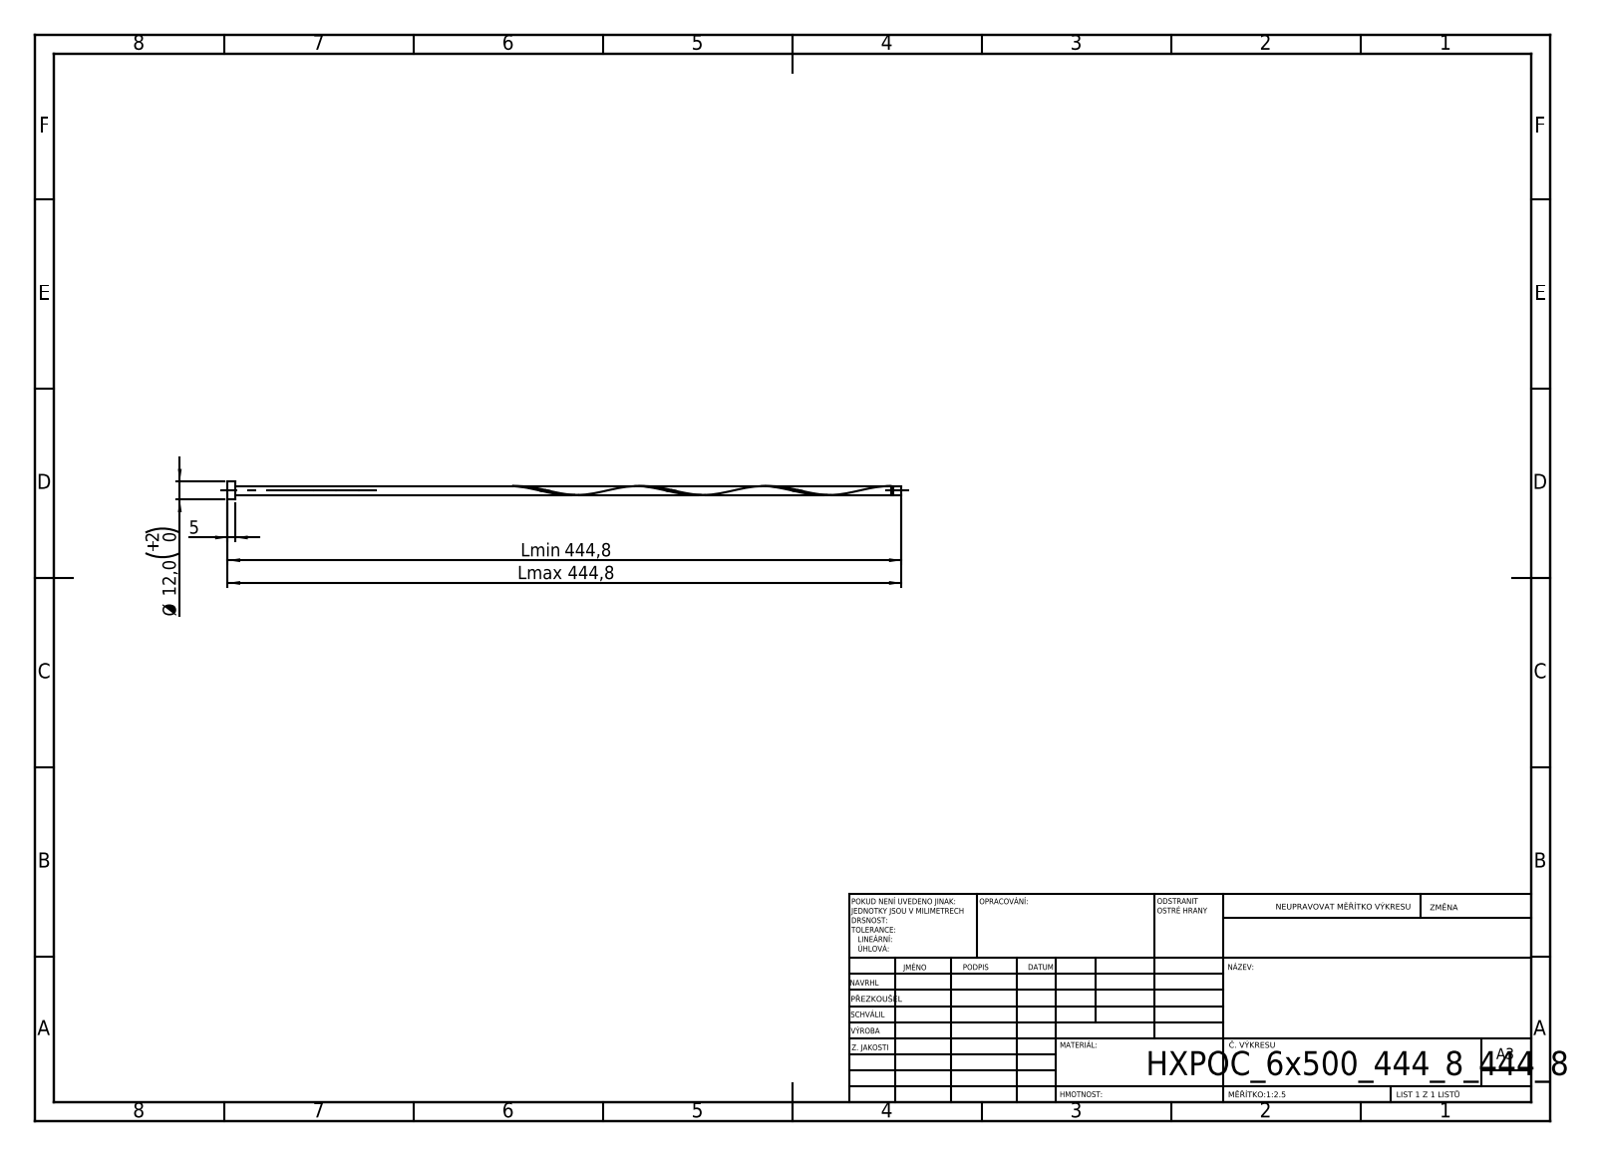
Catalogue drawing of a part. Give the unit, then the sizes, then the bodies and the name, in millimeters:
Units: millimetres
Overall size (bounding box): 444.8 × 12 × 12
Round bosses / shafts (diameter × count): ⌀12 ×1, ⌀6 ×1, ⌀4.8 ×1
Main face-to-face distances: 5, 444.8, 439.8, 438.98, 433.98, 5.82, 437.78, 432.78, 1.2, 7.02
Volume: 15 994 mm³ · Surface area: 12 008 mm²
Bodies: 1 solid, 16 faces (6 planar, 9 cylindrical, 1 other)
STEP written by: SolidWorks 2019 (CONFIG_CONTROL_DESIGN)
